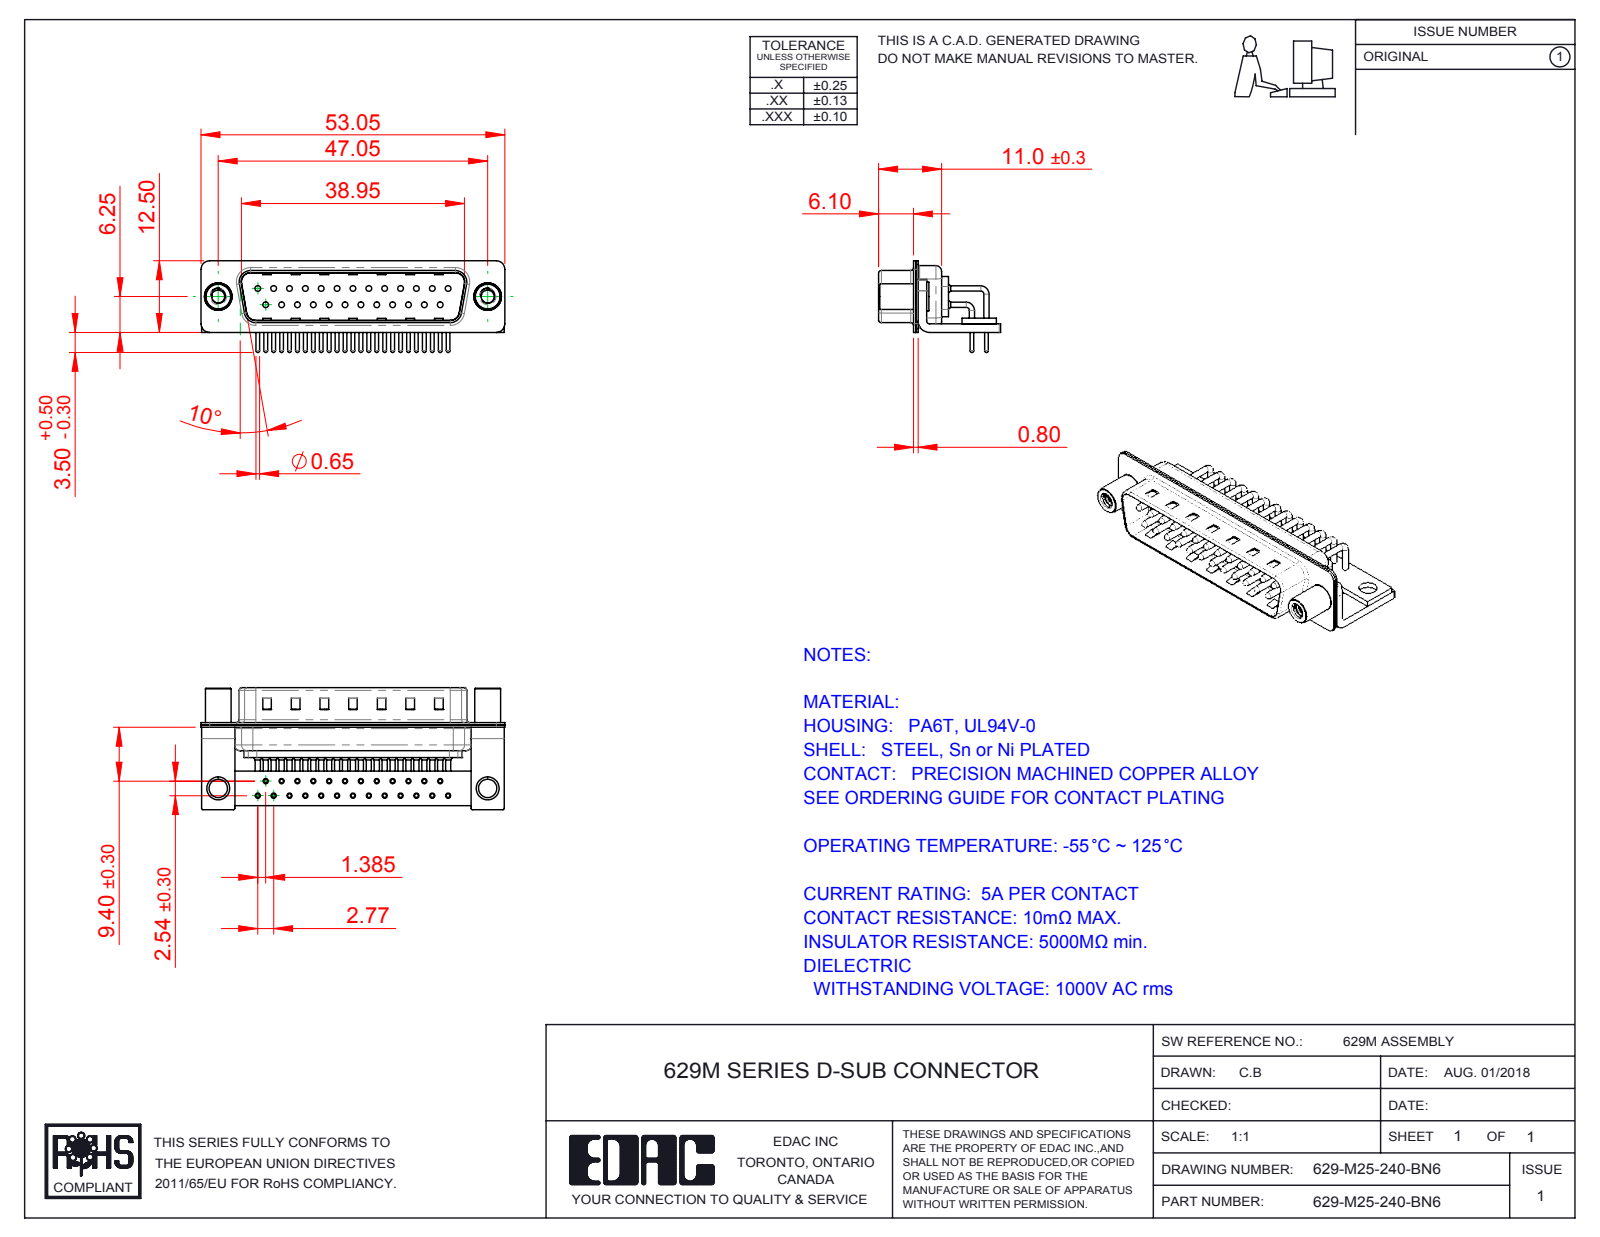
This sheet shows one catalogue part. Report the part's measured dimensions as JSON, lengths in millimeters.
{"part_name": "629M Contact Row 2; 629M Stabilizer Bracket; 629M 4-40 Threaded Standoff; 629M Housing_25 Contacts (+5 more)", "step_written_by": "SolidWorks 2016 (CONFIG_CONTROL_DESIGN)", "units": "millimeters", "bodies": {"solids": 33, "faces": 3276, "planar": 1799, "cylindrical": 1151, "other": 326}, "overall_size": [53.05, 21.3, 16], "volume_mm3": 3592, "surface_area_mm2": 9451, "round_holes": [[0.9, 25], [1, 25], [1.7, 25], [2, 25], [2.26, 2], [3.2, 2], [4, 2], [4.8, 2]], "round_bosses_or_shafts": [[1.5, 25], [0.9, 25], [0.65, 25], [5, 2], [4.9, 2], [4.5, 2]], "partial_cylinders_radius": [[1.01, 25], [0.25, 16], [1.5, 16], [2, 13], [0.5, 9], [1.6, 8], [0.6, 4], [0.65, 4]], "face_to_face_distances": [0.4, 0.85, 1.25, 1.5, 9.55, 0.8, 10.4, 8.3, 1, 1.9], "hole_center_spacings": [2.77, 5.54, 8.31, 11.08, 13.85, 3.16, 4.87, 16.62]}
